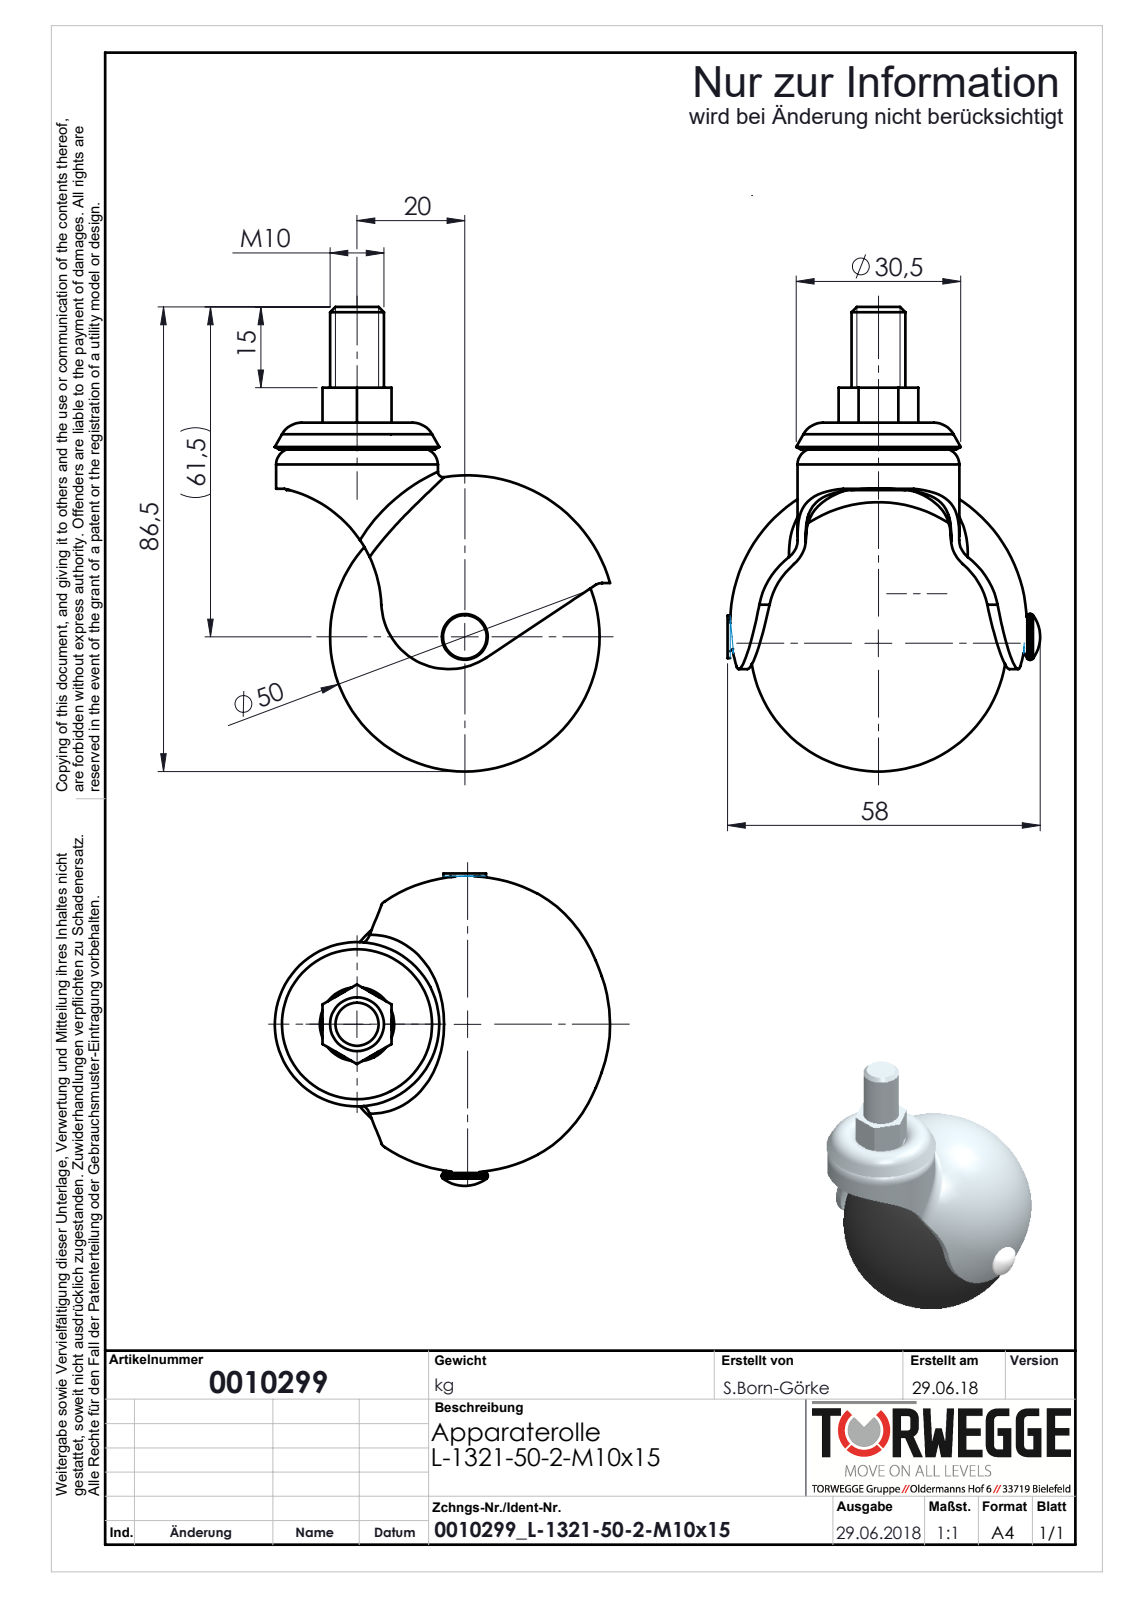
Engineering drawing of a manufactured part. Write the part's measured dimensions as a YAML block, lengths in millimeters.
part_name: "0010299_L-1321-50-2-M10x15"
step_written_by: "SolidWorks 2018 (AUTOMOTIVE_DESIGN)"
units: millimeters
bodies: {solids: 0, faces: 54, planar: 18, cylindrical: 14, other: 22}
overall_size: [86.25, 62.21, 58]
round_holes:
  - {diameter: 4, count: 1}
  - {diameter: 27, count: 1}
round_bosses_or_shafts:
  - {diameter: 30, count: 1}
  - {diameter: 26.1, count: 1}
  - {diameter: 10, count: 1}
  - {diameter: 9, count: 1}
  - {diameter: 8.5, count: 1}
  - {diameter: 7.9, count: 1}
partial_cylinders:
  - {radius: 2.01, count: 1}
  - {radius: 12.5, count: 1}
  - {radius: 23.03, count: 1}
face_to_face_distances: [12.8, 18.5, 33.5, 15, 47, 6, 12.5, 27.5, 0.5, 6.5]
